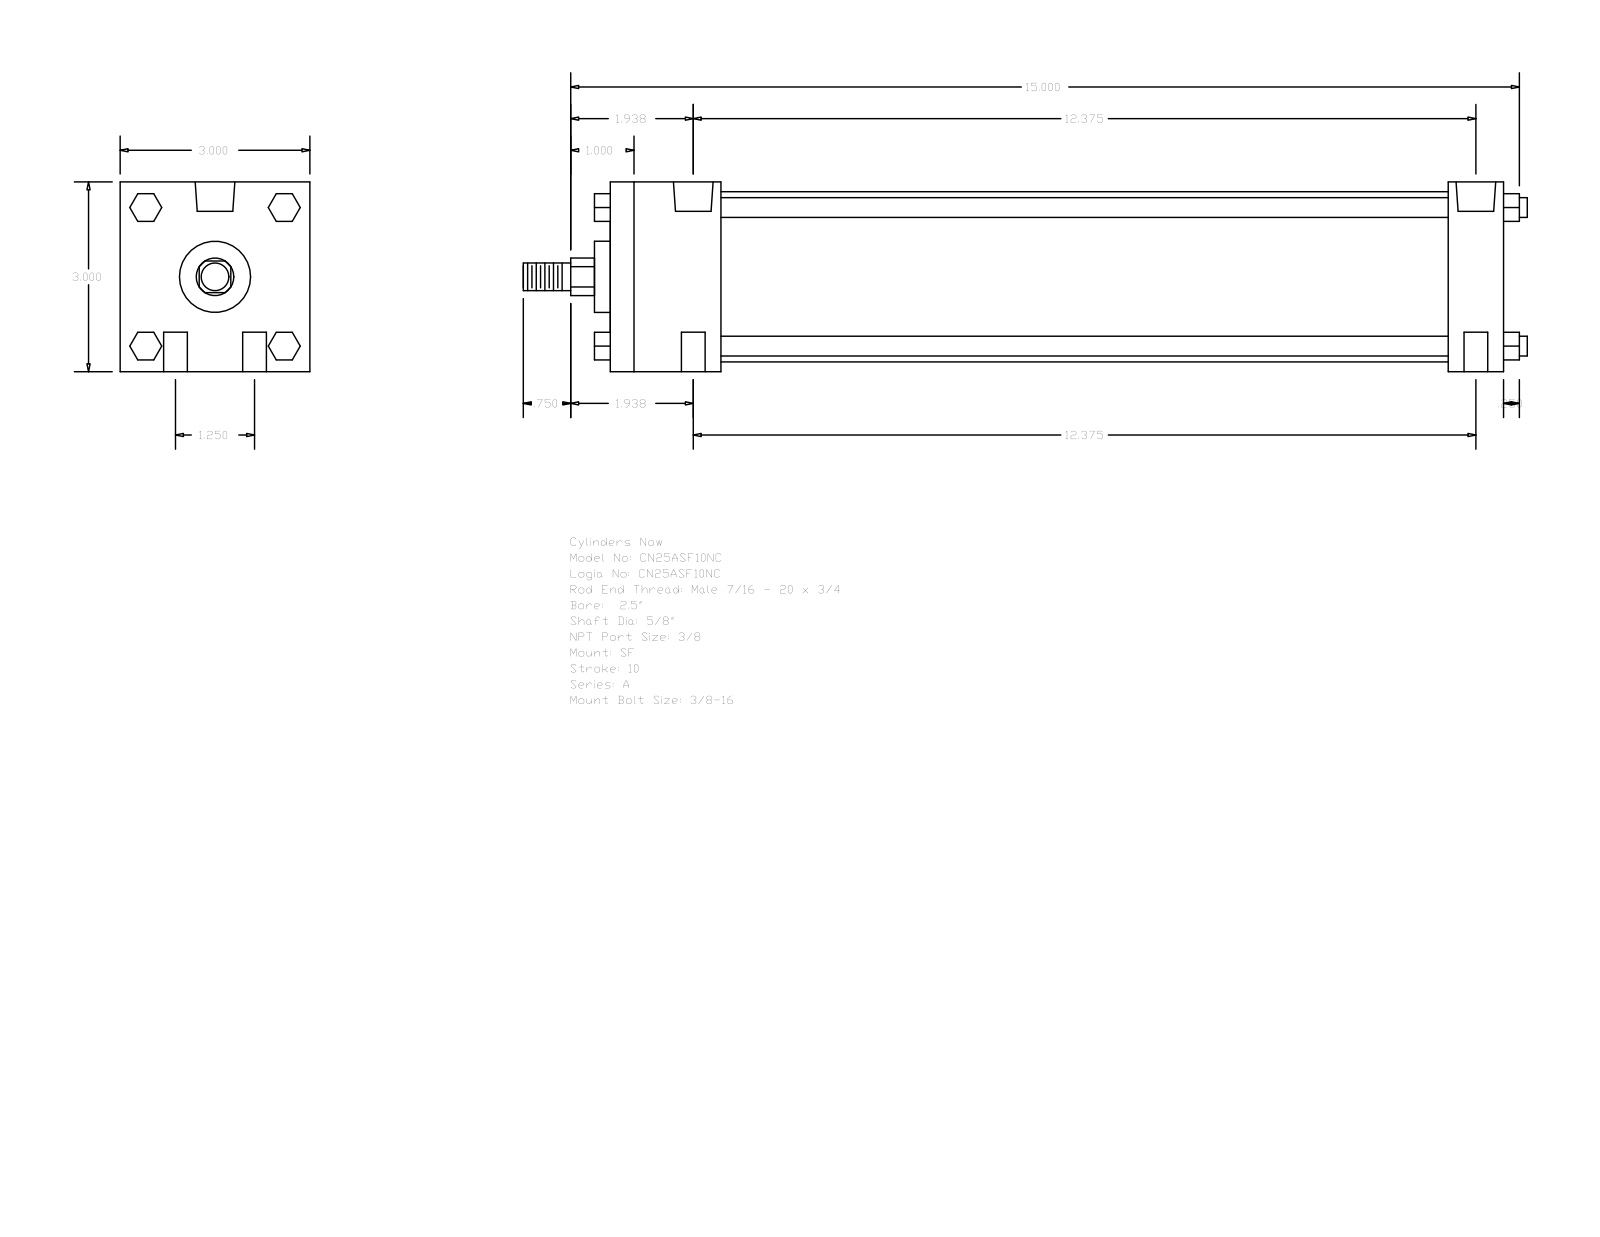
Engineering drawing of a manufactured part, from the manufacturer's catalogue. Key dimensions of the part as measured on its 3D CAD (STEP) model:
Part name (STEP PRODUCT): A_SF__0250_0.625
STEP written by: GSSL Pune (CONFIG_CONTROL_DESIGN)
Units: millimetres
Bodies: 0 solids, 124 faces (94 planar, 30 cylindrical, 0 other)
Overall size (bounding box): 403.23 × 76.2 × 76.2
Round holes (diameter × count): ⌀9.53 ×4, ⌀5.56 ×2, ⌀15.93 ×2
Round bosses / shafts (diameter × count): ⌀7.94 ×4, ⌀68.33 ×1, ⌀28.57 ×1, ⌀15.88 ×1, ⌀11.11 ×1
Partial cylindrical surfaces — rounded edges, fillets, slot ends (radius × count): R7.54 ×1
Main face-to-face distances: 76.2, 358.77, 44.45, 336.55, 22.22, 292.1, 314.32, 6.35, 365.12, 50.8
Hole centre spacings: 15.88, 314.73, 314.33, 31.76, 315.93, 319.09
